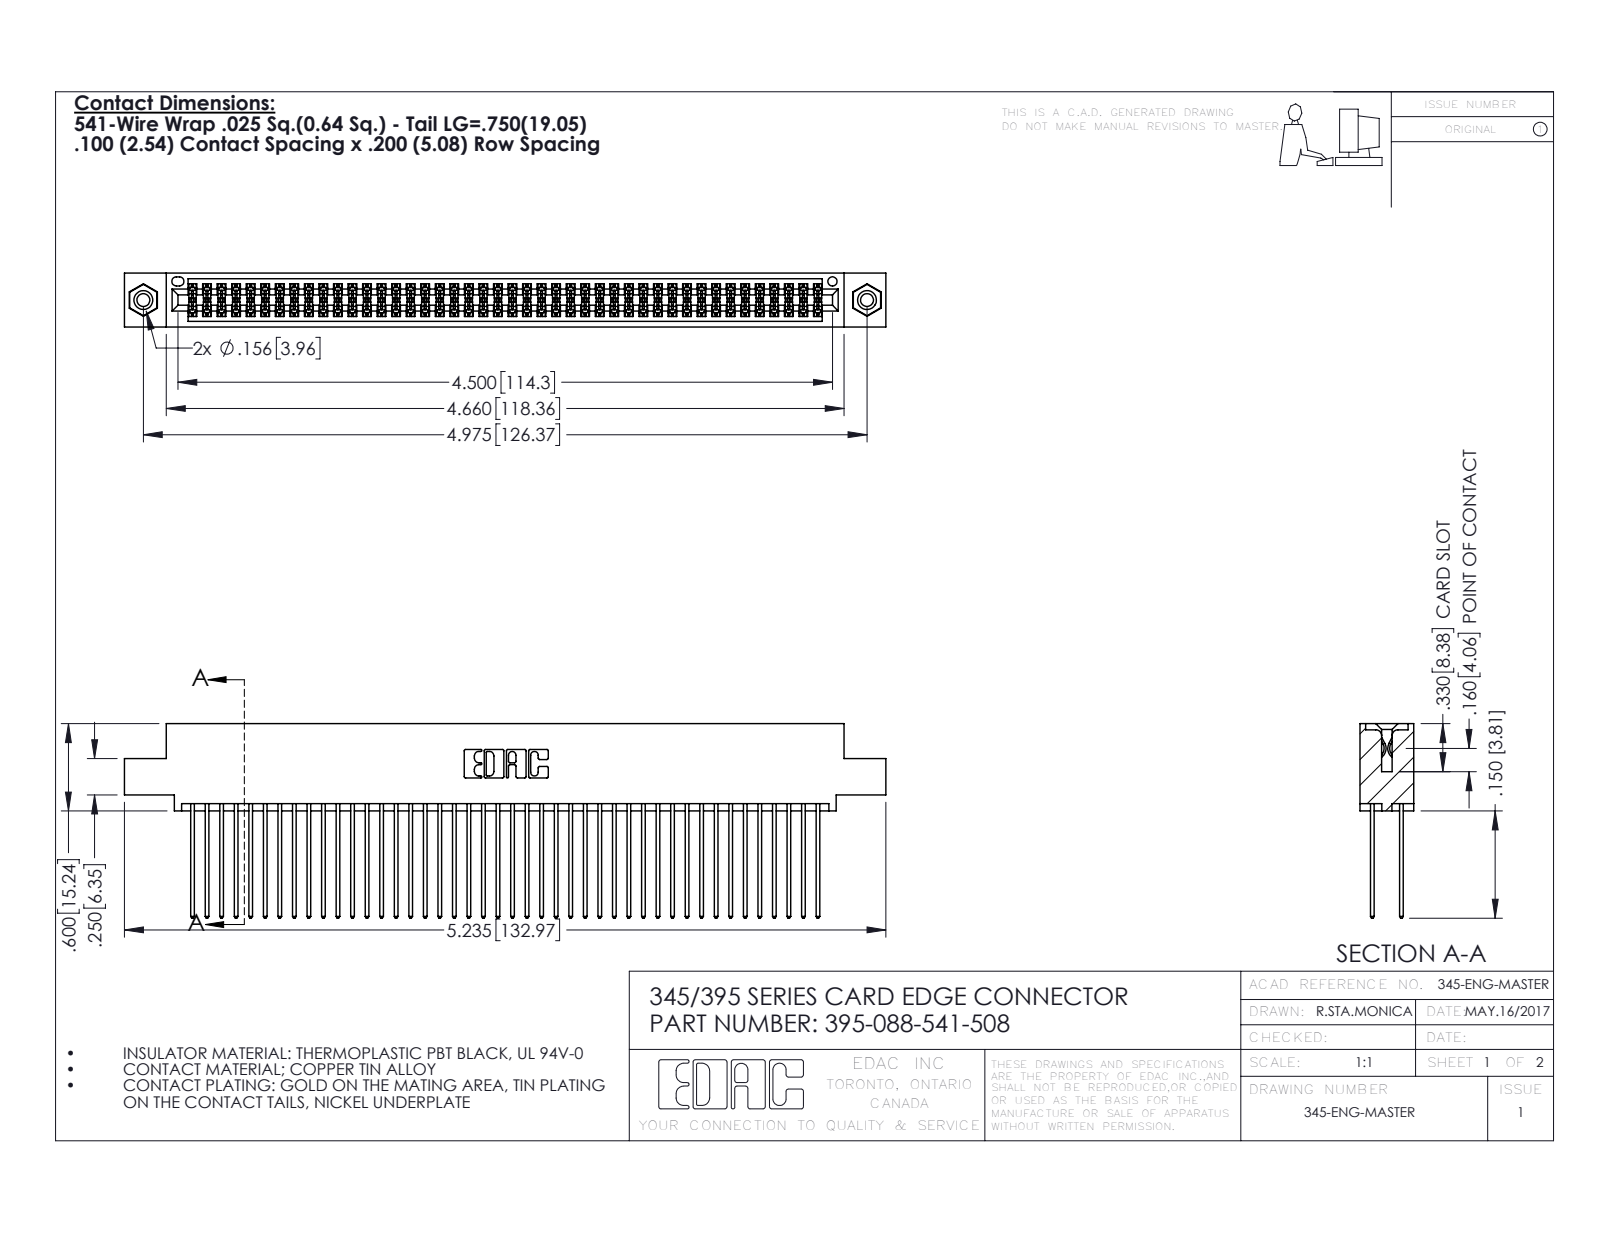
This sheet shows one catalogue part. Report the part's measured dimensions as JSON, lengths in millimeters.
{"part_name": "345 Part_0.110 Offset - 0.156 Dia-TI; 395-088-541-508; 345-292-001_345-293-141; 345-250-001_345-250-003-102", "step_written_by": "SolidWorks 2016 (CONFIG_CONTROL_DESIGN)", "units": "millimeters", "bodies": {"solids": 91, "faces": 4590, "planar": 3020, "cylindrical": 1554, "other": 16}, "overall_size": [133, 34, 9.4], "volume_mm3": 13400, "surface_area_mm2": 22260, "round_holes": [[2.3, 2], [3.2, 2], [4, 2], [1.6, 1]], "round_bosses_or_shafts": [[3.9, 2]], "partial_cylinders_radius": [[0.2, 132], [0.3, 88], [0.3, 22], [0.2, 6], [0.8, 6], [0.7, 3], [0.4, 2], [0.5, 2]], "face_to_face_distances": [1.8, 7.6, 5.1, 2.5, 6.9, 0.6, 5.7, 9.4, 4.4, 3.8], "hole_center_spacings": [6.9, 120.4, 126.4]}
